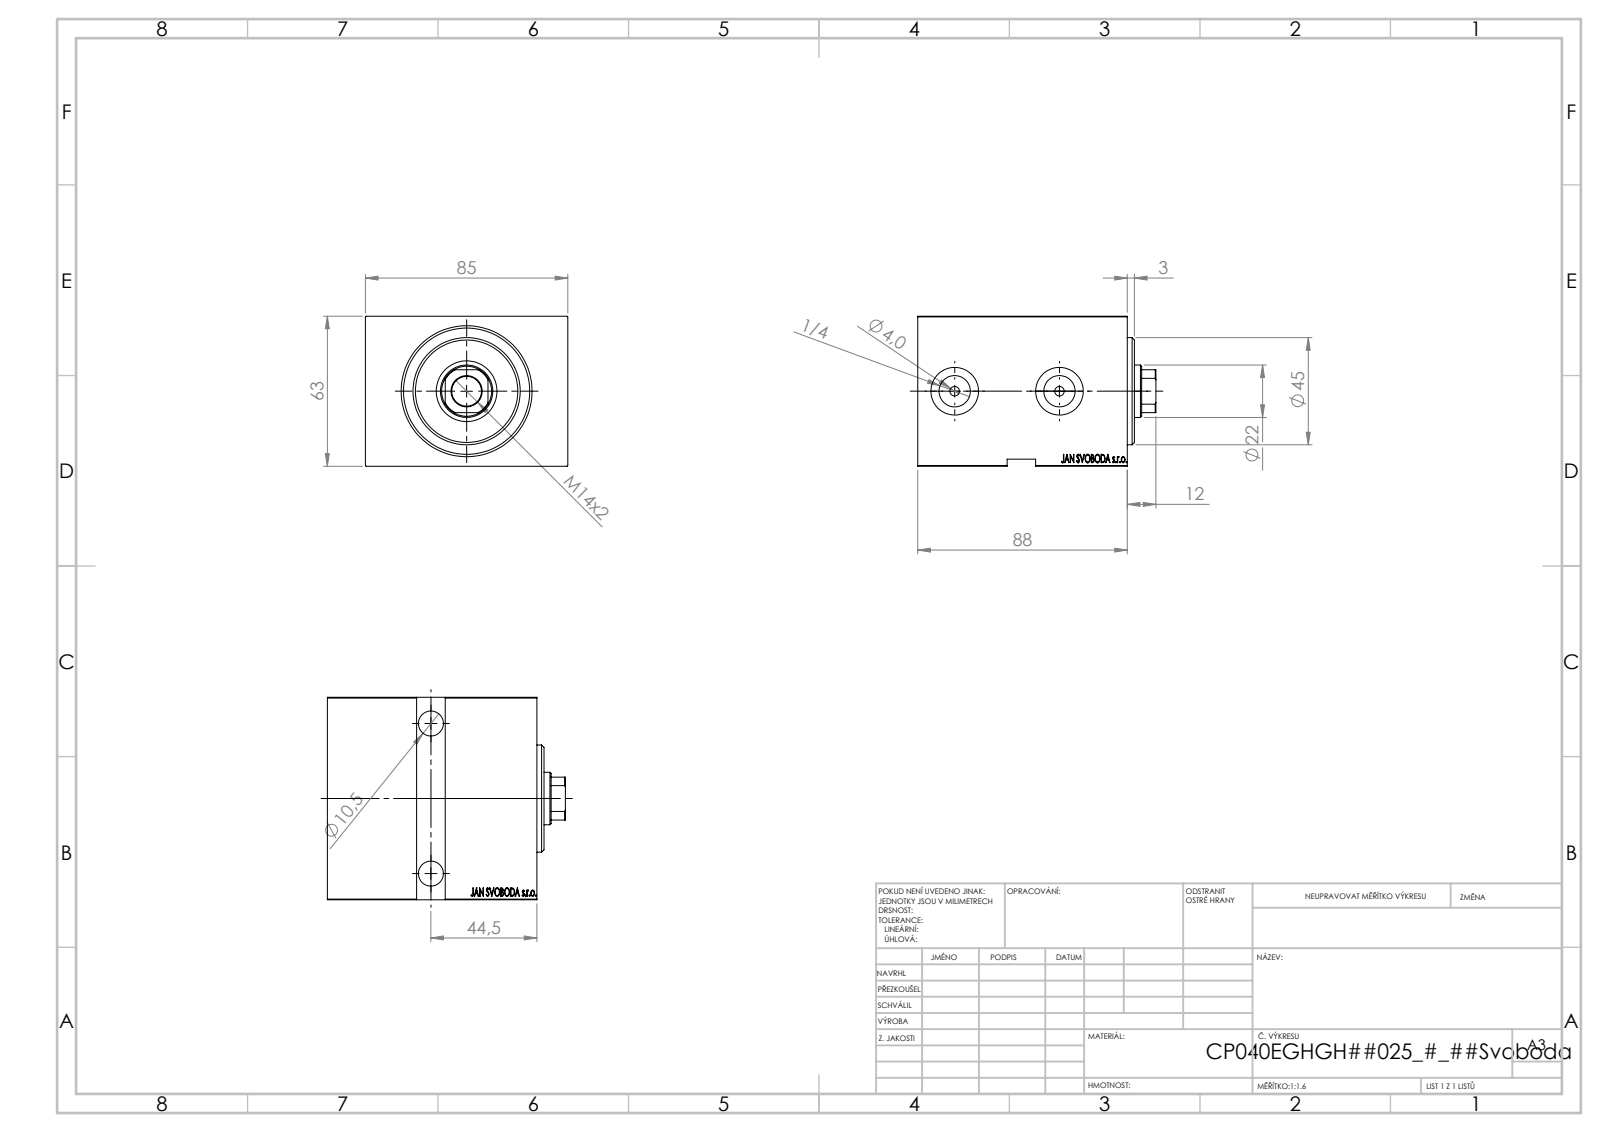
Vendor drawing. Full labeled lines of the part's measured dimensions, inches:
Part name (STEP PRODUCT): V450CM_E_Body; V450CM_E_VCP; V450CM_VC_B
STEP written by: SolidWorks 2019 (CONFIG_CONTROL_DESIGN)
Units: inches
Bodies: 3 solids, 846 faces (408 planar, 44 cylindrical, 394 other)
Overall size (bounding box): 3.937 × 3.346 × 2.48
Volume: 26.73 in³ · Surface area: 111.1 in²
Round holes (diameter × count): ⌀0.157 ×2, ⌀0.413 ×2, ⌀0.518 ×2, ⌀0.65 ×2, ⌀0.787 ×2, ⌀0.492 ×1, ⌀0.866 ×1, ⌀1.004 ×1, ⌀1.575 ×1, ⌀2.087 ×1
Round bosses / shafts (diameter × count): ⌀1.772 ×1, ⌀1.654 ×1
Partial cylindrical surfaces — rounded edges, fillets, slot ends (radius × count): R0.413 ×1
Main face-to-face distances: 2.48, 3.346, 3.465, 0.472, 2.992, 0.118, 0.197, 3.268, 2.795, 1.575
Hole centre spacings: 1.732, 2.48
